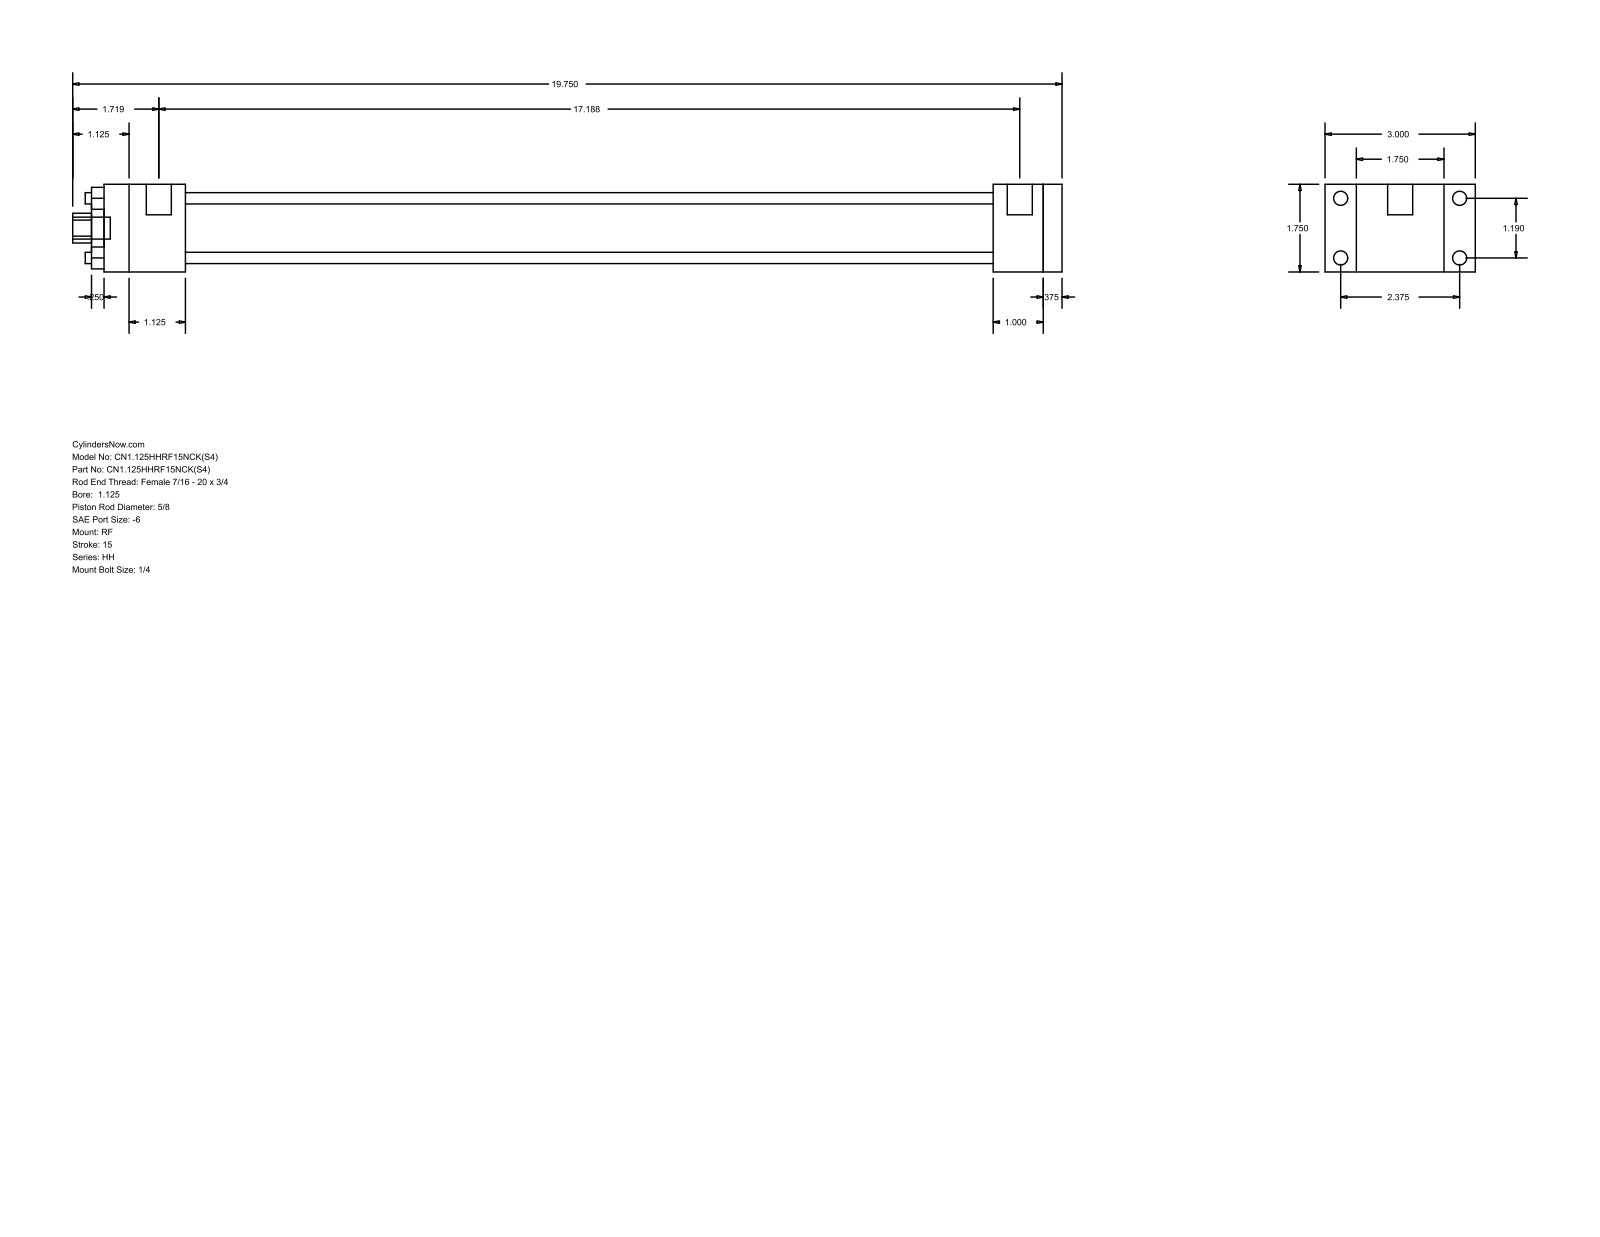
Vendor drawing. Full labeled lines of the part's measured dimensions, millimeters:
Part name (STEP PRODUCT): HH_RF__0112_0.625
STEP written by: GSSL Pune (CONFIG_CONTROL_DESIGN)
Units: millimetres
Bodies: 0 solids, 92 faces (64 planar, 28 cylindrical, 0 other)
Overall size (bounding box): 501.65 × 76.2 × 44.45
Round holes (diameter × count): ⌀5.71 ×4, ⌀15.88 ×1, ⌀28.57 ×1, ⌀34.92 ×1
Round bosses / shafts (diameter × count): ⌀7.14 ×4, ⌀5.56 ×4, ⌀12.7 ×2, ⌀11.11 ×1
Partial cylindrical surfaces — rounded edges, fillets, slot ends (radius × count): R7.54 ×1
Main face-to-face distances: 44.46, 9.53, 485.77, 15.87, 434.97, 444.5, 409.58, 25.39, 34.92, 41.27
Hole centre spacings: 21.37, 30.22, 42.74
